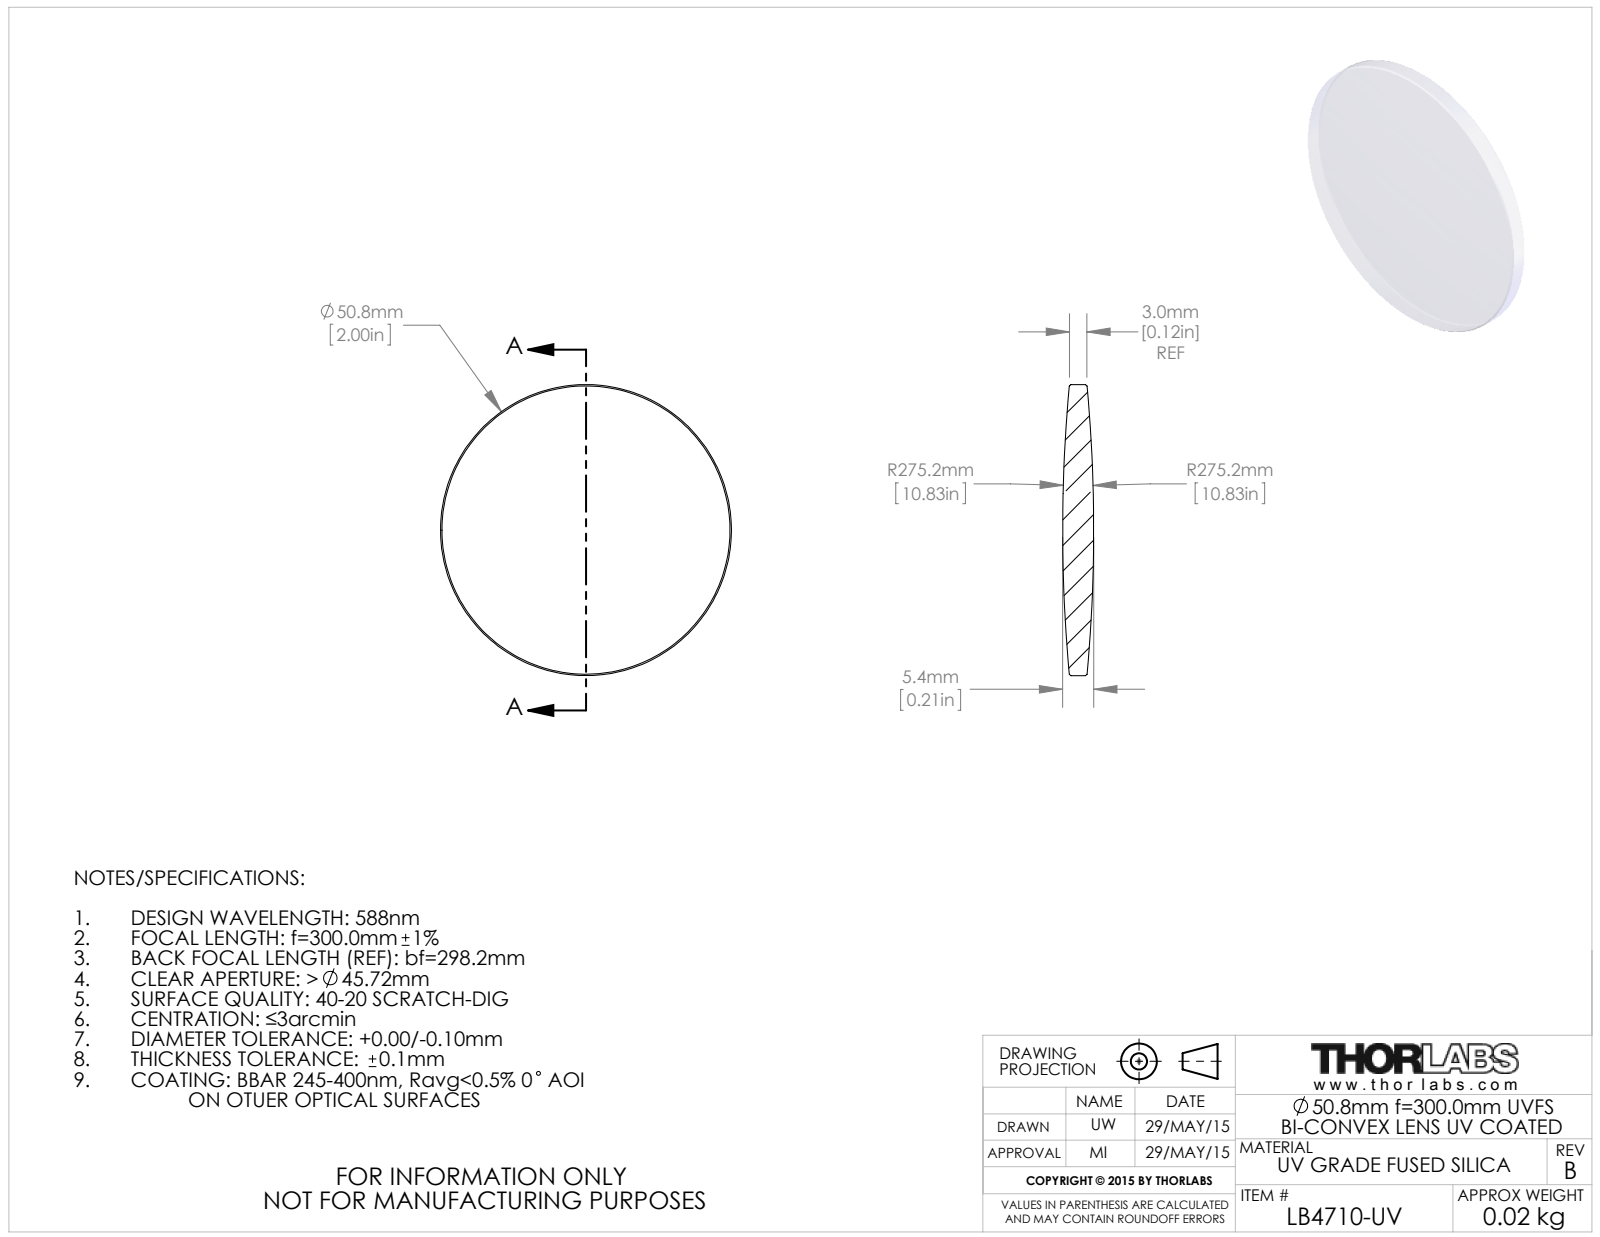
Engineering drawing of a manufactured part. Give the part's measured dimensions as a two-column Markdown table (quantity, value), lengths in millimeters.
| quantity | value |
| --- | --- |
| part name | 4337-E0W |
| STEP written by | SolidWorks 2014 (CONFIG_CONTROL_DESIGN) |
| units | millimeters |
| bodies | 1 solid, 10 faces (0 planar, 2 cylindrical, 8 other) |
| overall size | 50.8 × 50.8 × 5.4 |
| volume | 8 556 mm³ |
| surface area | 4 507 mm² |
| round bosses / shafts (diameter × count) | 50.8 × 1 |
